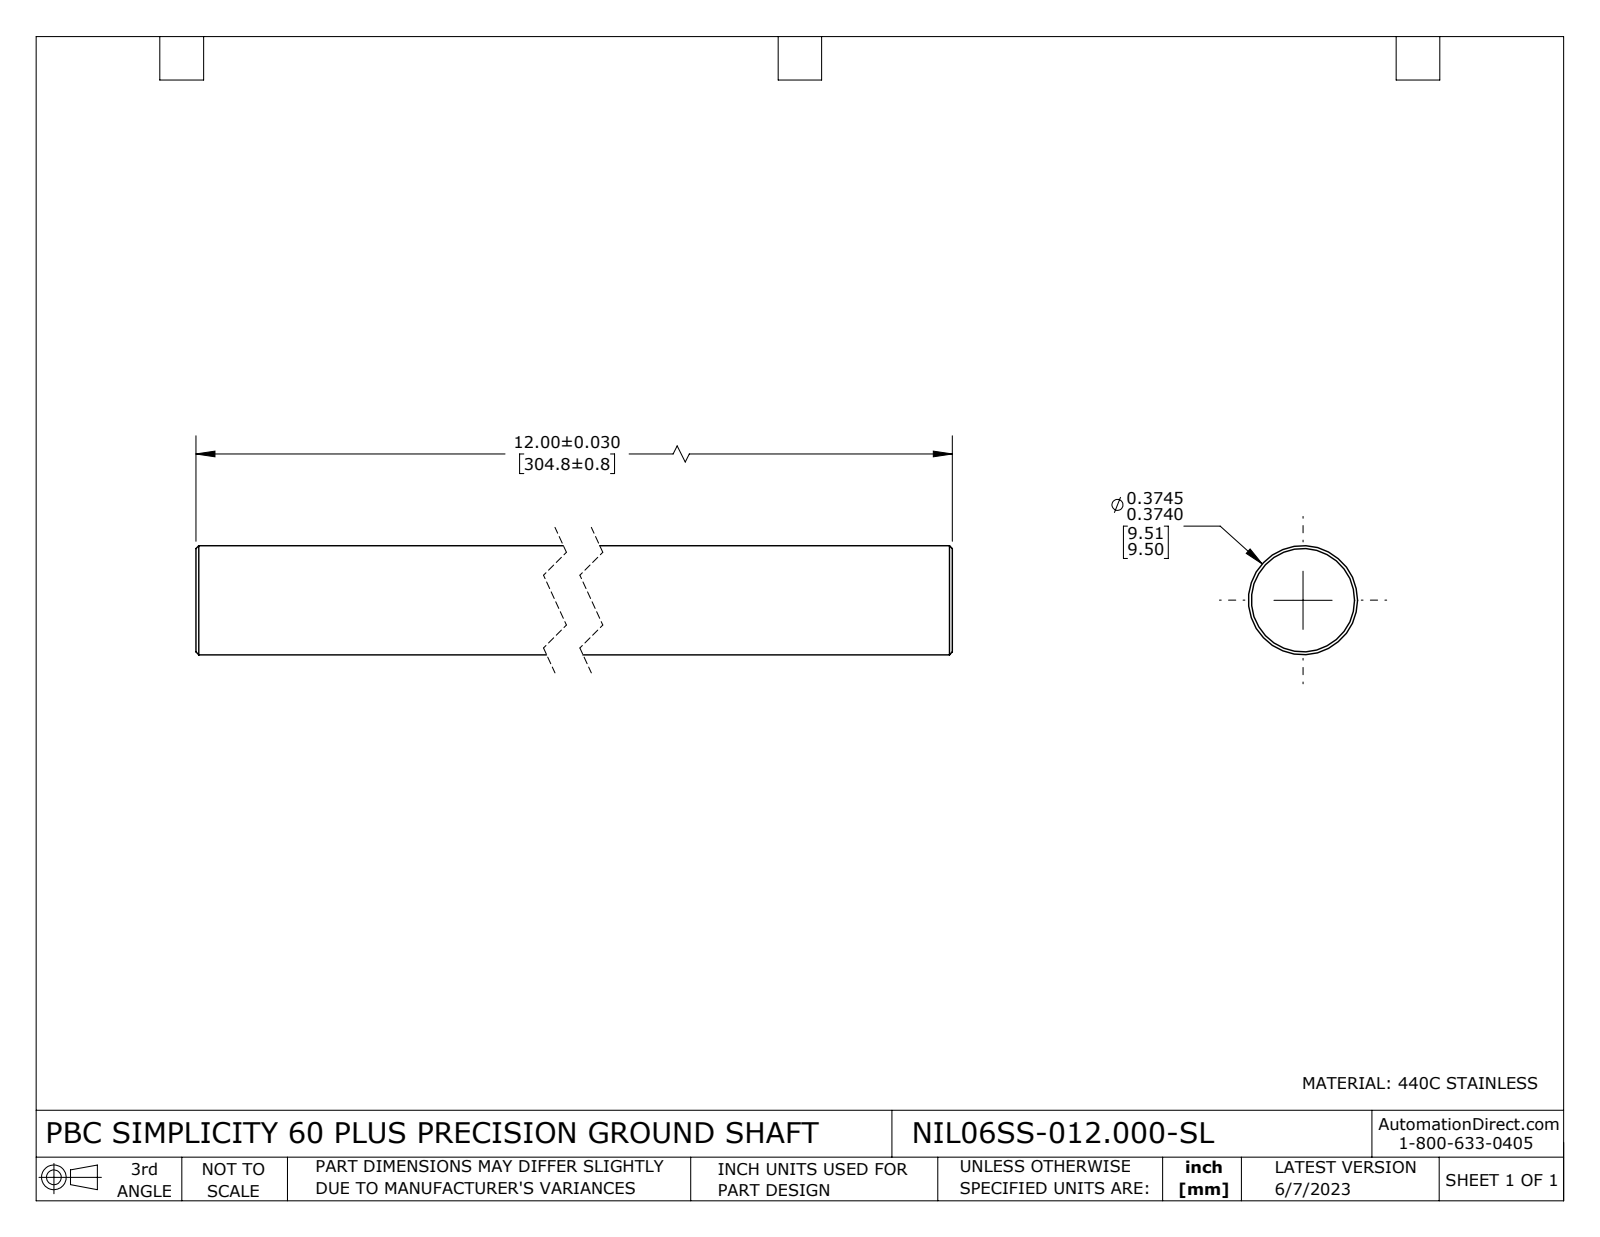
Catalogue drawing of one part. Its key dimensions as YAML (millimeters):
part_name: "NIL06SS-012.000-SL"
step_written_by: "SolidWorks 2021 (CONFIG_CONTROL_DESIGN)"
units: millimeters
bodies: {solids: 1, faces: 8, planar: 2, cylindrical: 2, other: 4}
overall_size: [304.8, 9.5, 9.5]
volume: 21710
surface_area: 9252
round_bosses_or_shafts:
  - {diameter: 9.5, count: 1}
face_to_face_distances: [304.8]
